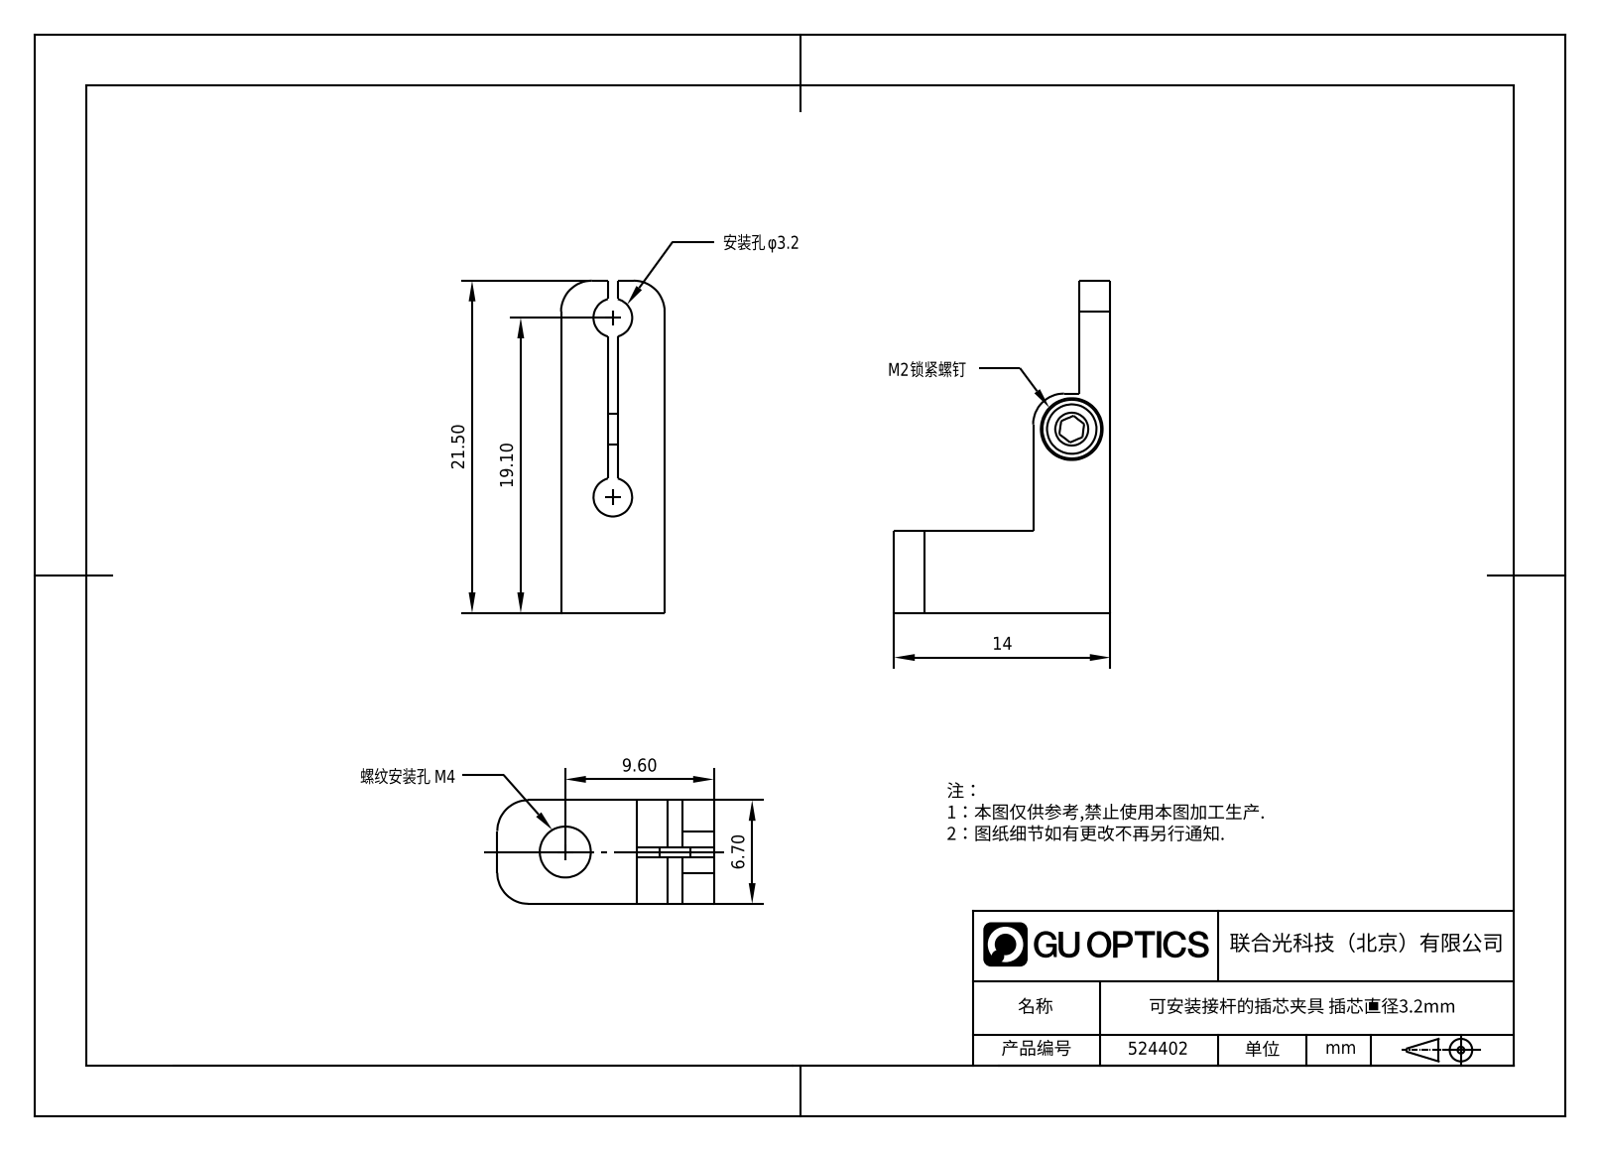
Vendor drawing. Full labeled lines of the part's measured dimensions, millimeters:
Part name (STEP PRODUCT): 1.8.3.9-ZFJ-CM32; 30.1.圆柱头内六角不锈钢螺丝_30.1.16-M2*4; 可安装接杆的插芯夹具主体，M4螺孔_1.8.3.9.1-ZFJ-CM32
STEP written by: SolidWorks 2021 (CONFIG_CONTROL_DESIGN)
Units: millimetres
Bodies: 2 solids, 60 faces (28 planar, 24 cylindrical, 8 other)
Overall size (bounding box): 21.5 × 14 × 6.7
Volume: 761 mm³ · Surface area: 945 mm²
Round holes (diameter × count): ⌀1.6 ×1, ⌀2.4 ×1, ⌀2.5 ×1, ⌀3.2 ×1, ⌀3.3 ×1, ⌀4 ×1
Round bosses / shafts (diameter × count): ⌀3.8 ×1, ⌀2 ×1
Partial cylindrical surfaces — rounded edges, fillets, slot ends (radius × count): R2 ×5
Main face-to-face distances: 6.7, 3.03, 3.67, 5.3, 5, 2, 3, 0.64, 9, 12
Hole centre spacings: 11.6
